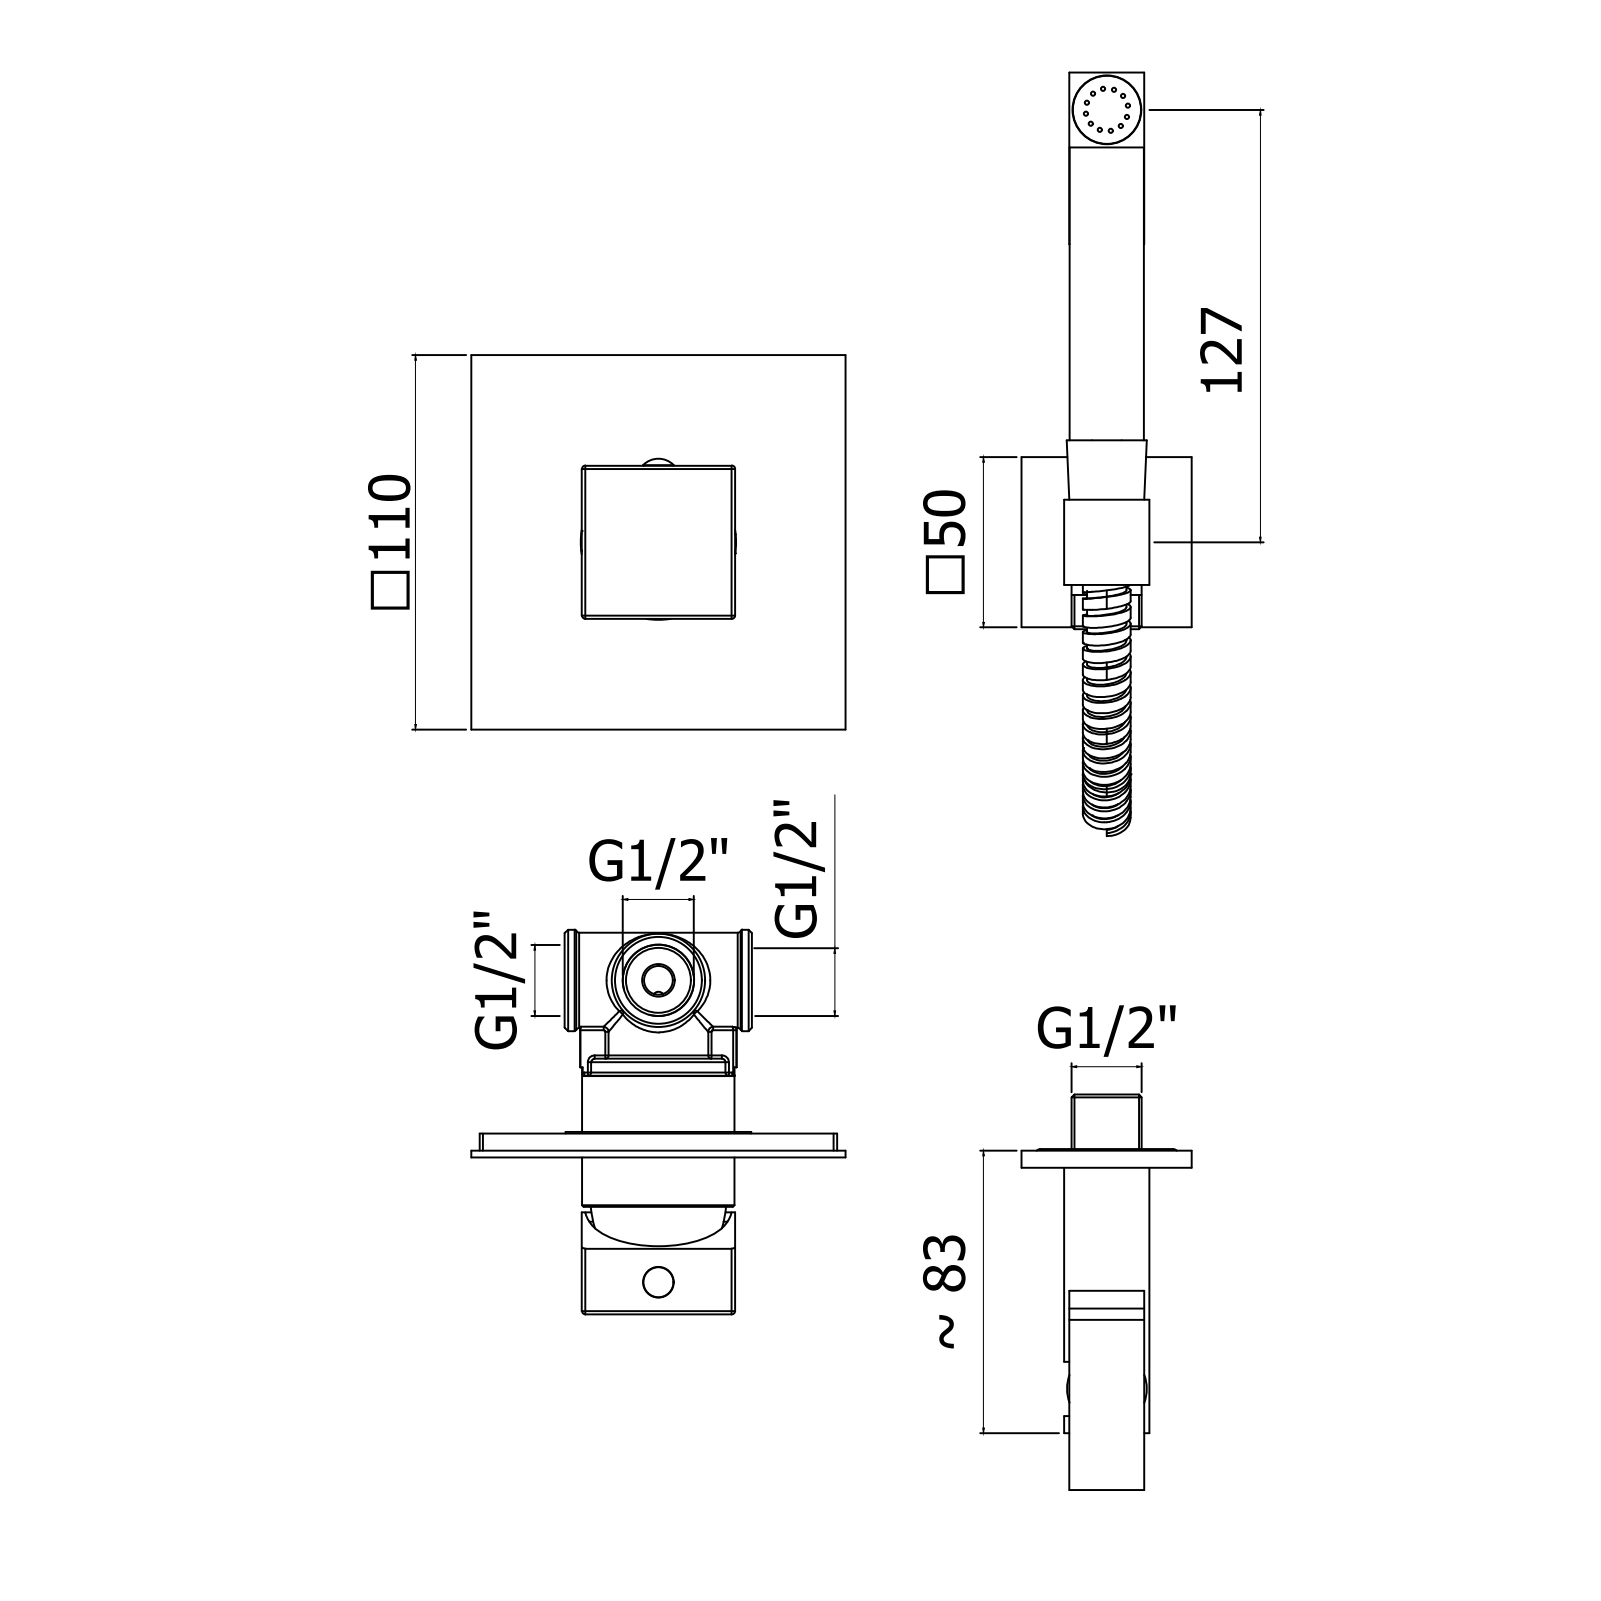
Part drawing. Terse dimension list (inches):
name: KITDUP112CR
written by: CREO PARAMETRIC BY PTC INC, 2020044 (CONFIG_CONTROL_DESIGN)
unit: in
bodies: 5 solids, 1151 faces (679 planar, 263 cylindrical, 209 other)
size: 9.055 × 8.831 × 3.925
volume: 11.71 in³; area: 163.7 in²
holes: 12× ⌀0.047, 2× ⌀0.157, 2× ⌀0.591, 2× ⌀0.748, 2× ⌀1.654, 1× ⌀0.13, 1× ⌀0.197, 1× ⌀0.236, 1× ⌀0.433, 1× ⌀0.472, 1× ⌀0.768, 1× ⌀0.783
bosses: 2× ⌀0.811, 1× ⌀1.764, 1× ⌀1.417, 1× ⌀1.378, 1× ⌀0.925, 1× ⌀0.921, 1× ⌀0.866, 1× ⌀0.858
rounds: 11× R0.006, 10× R0.039, 6× R0.02, 4× R0.012, 2× R0.083, 2× R0.098, 1× R0.156, 1× R0.207
face distances: 0.079, 0.118, 0.063, 0.858, 0.921, 0.984, 1.697, 0.059, 0.925, 0.862
hole spacings: 0.246, 0.127, 0.348, 0.426, 0.475, 0.128, 0.246, 0.348
